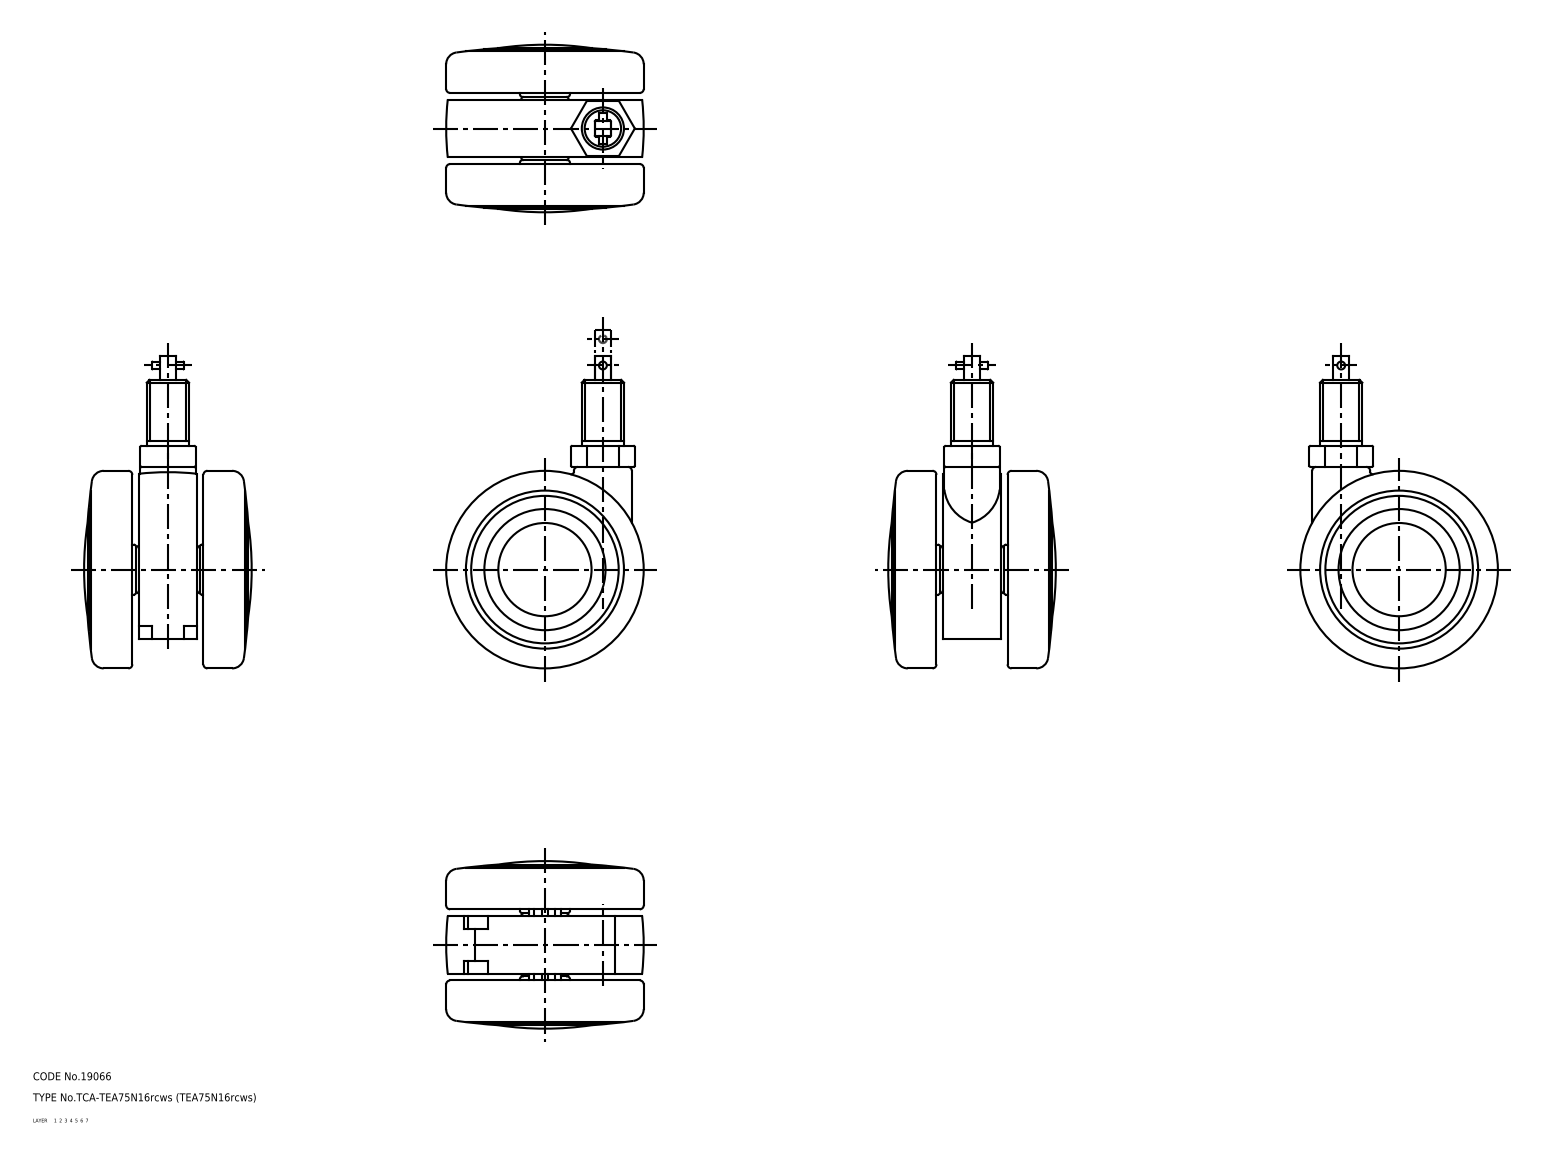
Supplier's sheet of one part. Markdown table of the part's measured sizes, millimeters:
| quantity | value |
| --- | --- |
| part name | wheel_mr; wheel; main shaft; TEA75N16rcws_5416_36 |
| STEP written by | CADfix (AUTOMOTIVE_DESIGN) |
| units | millimeters |
| bodies | 4 solids, 184 faces (0 planar, 0 cylindrical, 184 other) |
| overall size | 118.5 × 75 × 63.62 |
| volume | 218 153 mm³ |
| surface area | 52 007 mm² |
